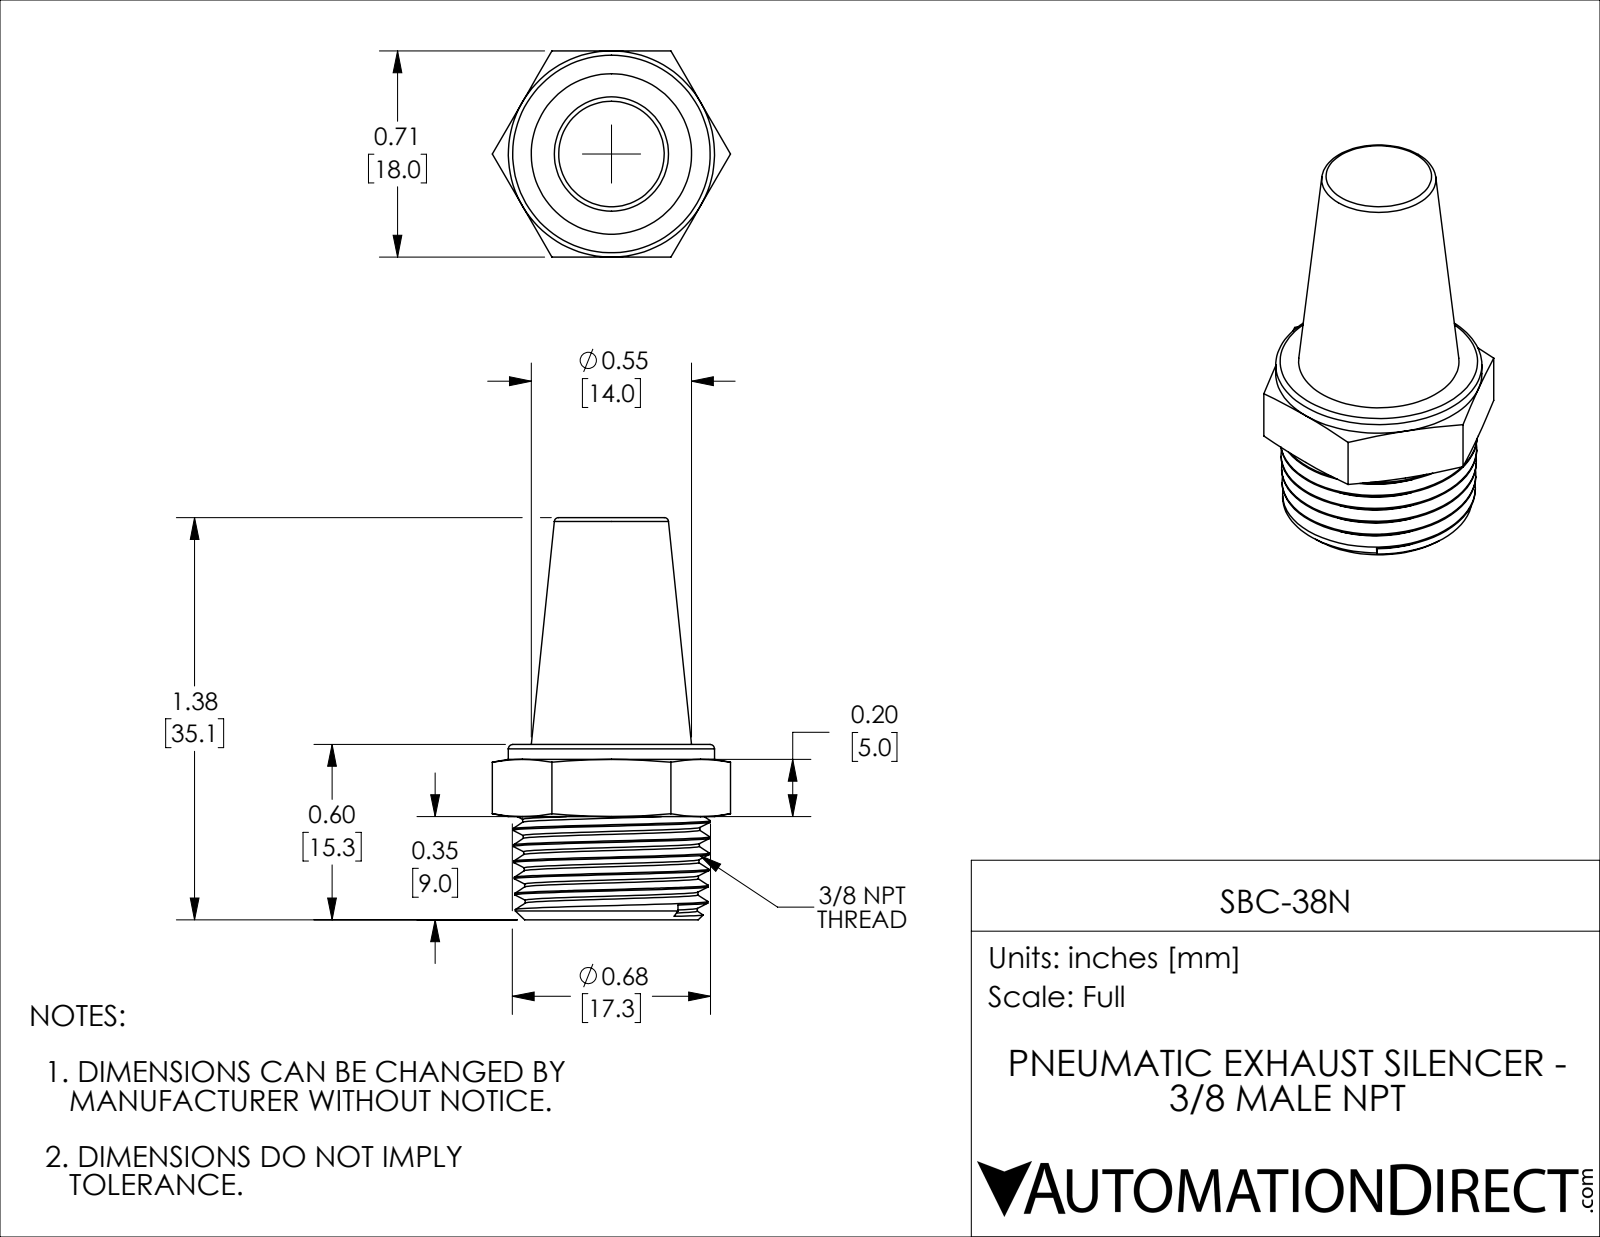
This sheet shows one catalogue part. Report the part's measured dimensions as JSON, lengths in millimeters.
{"part_name": "SBC-38N", "step_written_by": "SolidWorks 2021 (CONFIG_CONTROL_DESIGN)", "units": "millimeters", "bodies": {"solids": 1, "faces": 52, "planar": 12, "cylindrical": 4, "other": 36}, "overall_size": [35.1, 20.8, 18], "volume_mm3": 5160, "surface_area_mm2": 2656, "round_holes": [[8, 1]], "round_bosses_or_shafts": [[18, 1]], "face_to_face_distances": [18, 15.3, 35.1, 19.8, 12.7, 2.6, 22.4, 9, 3.7, 6.3]}
